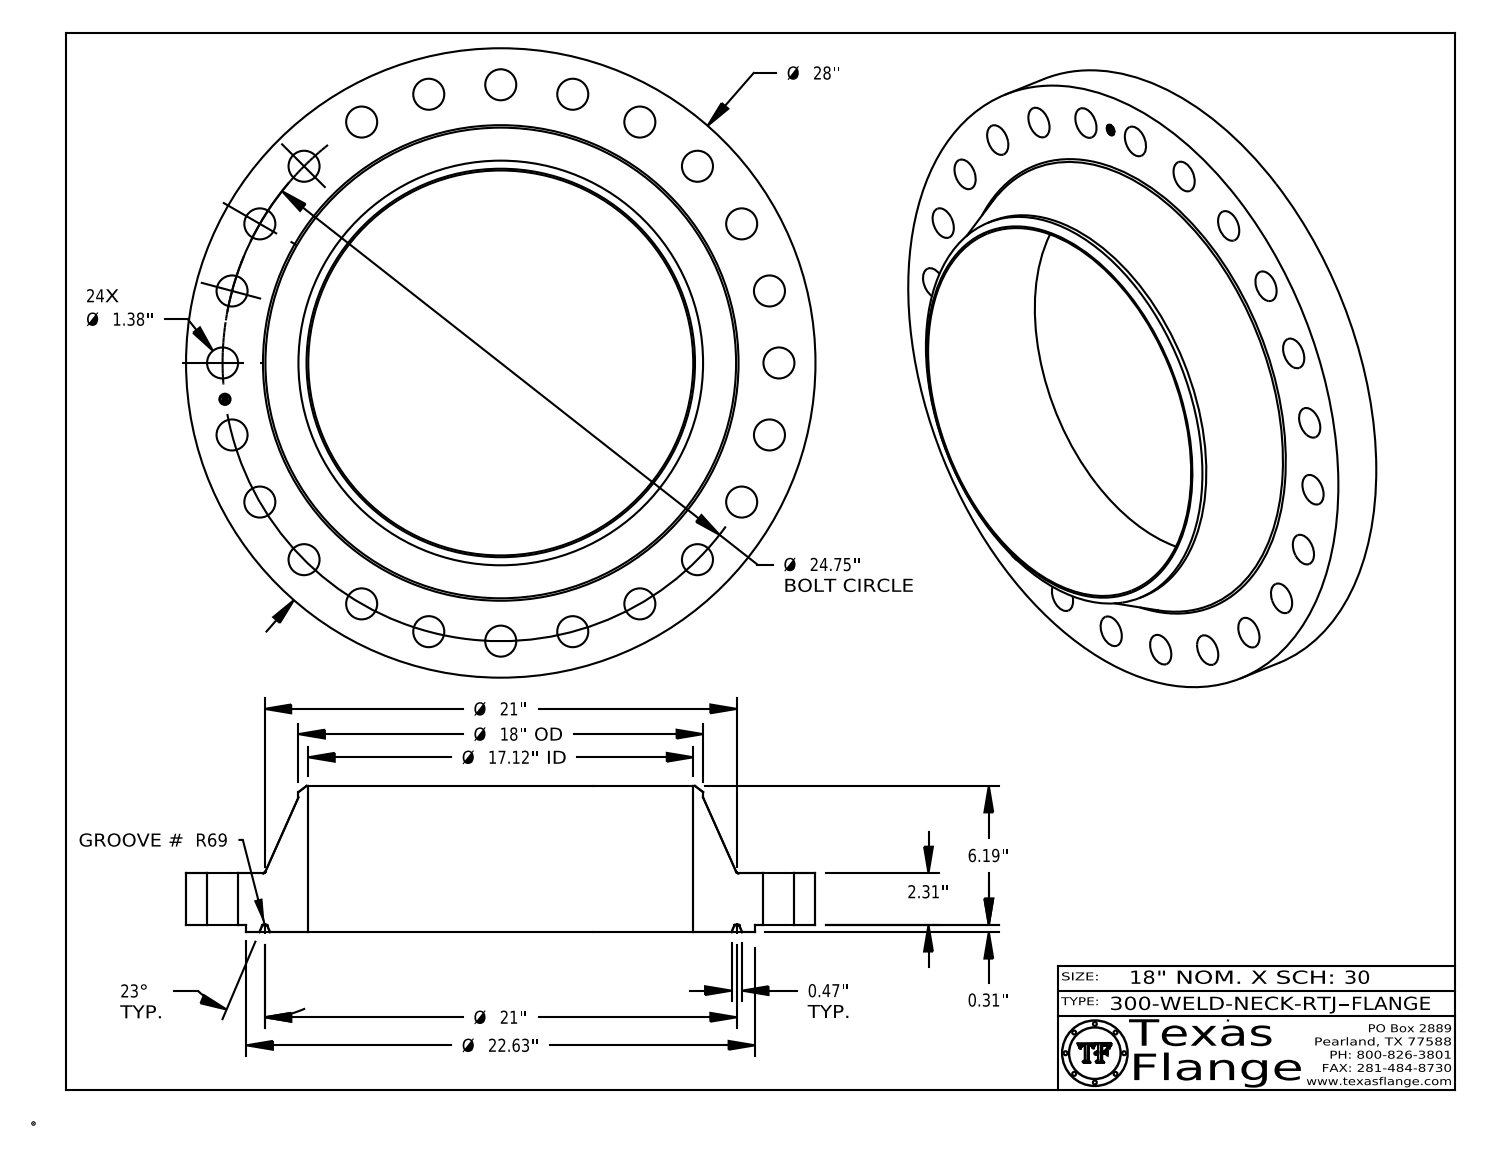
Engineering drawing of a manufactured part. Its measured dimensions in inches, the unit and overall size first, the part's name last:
Units: inches
Overall size (bounding box): 28 × 28 × 6.503
Round holes (diameter × count): ⌀1.38 ×24, ⌀0.495 ×1, ⌀17.124 ×1
Round bosses / shafts (diameter × count): ⌀0.03 ×8, ⌀28 ×1, ⌀22.625 ×1, ⌀18 ×1, ⌀0.39 ×1
Main face-to-face distances: 2.31, 0.313, 2.623, 6.503, 6.19, 3.88, 2.608, 2.295, 0.015, 3.895
Hole centre spacings: 12.375, 9.471, 15.067, 17.501, 21.434, 22.866, 23.906, 3.23
Volume: 1 096 in³ · Surface area: 1 693 in²
Bodies: 1 solid, 461 faces (371 planar, 76 cylindrical, 14 other)
Part name (STEP PRODUCT): 300-WELD-NECK-RTJ
STEP written by: CATIA V5 STEP AP214 (AUTOMOTIVE_DESIGN)
